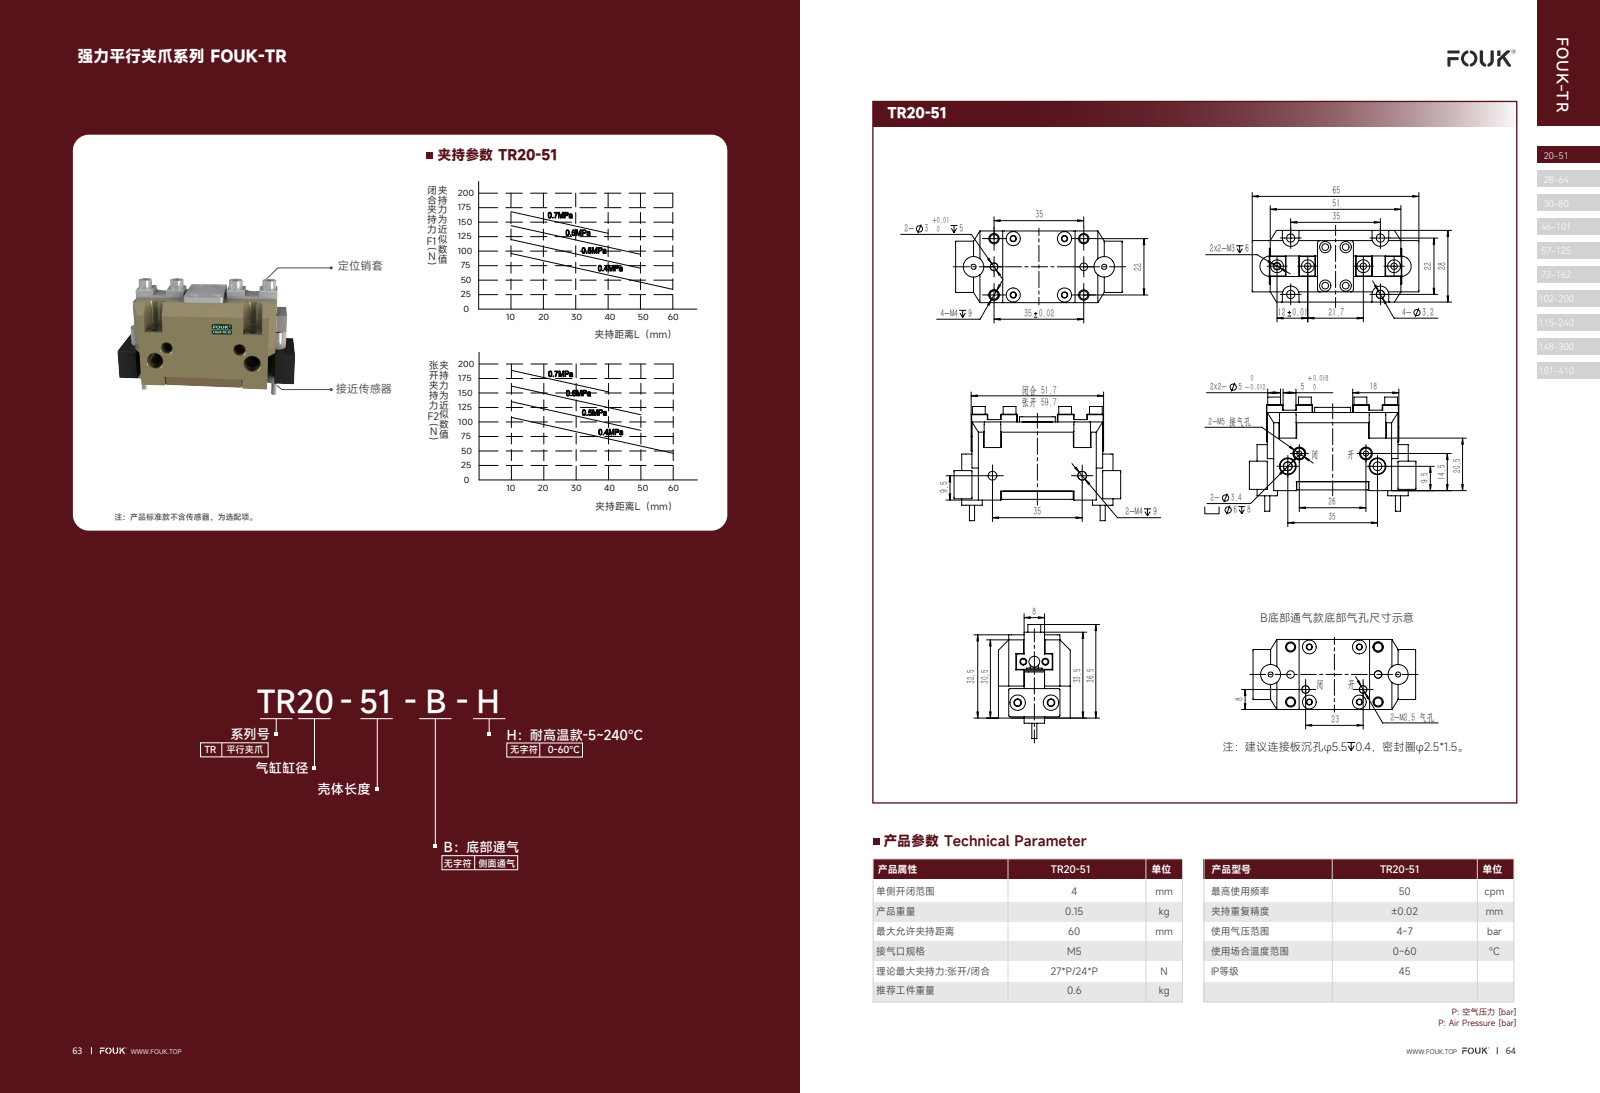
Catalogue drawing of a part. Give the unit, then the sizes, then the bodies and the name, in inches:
Units: inches
Overall size (bounding box): 2.559 × 1.871 × 1.102
Round holes (diameter × count): ⌀0.118 ×7, ⌀0.098 ×6, ⌀0.13 ×6, ⌀0.102 ×5, ⌀0.087 ×4, ⌀0.126 ×4, ⌀0.197 ×4, ⌀0.236 ×4, ⌀0.081 ×3, ⌀0.079 ×2, ⌀0.083 ×2, ⌀0.106 ×2
Round bosses / shafts (diameter × count): ⌀0.079 ×4, ⌀0.15 ×2, ⌀0.063 ×1, ⌀0.028 ×1
Partial cylindrical surfaces — rounded edges, fillets, slot ends (radius × count): R0.005 ×30, R0.079 ×8, R0.039 ×6, R0.012 ×5, R0.02 ×4, R0.128 ×4, R0.006 ×2, R0.02 ×2
Main face-to-face distances: 0.118, 0.276, 0.709, 0.394, 0.433, 0.827, 0.453, 1.102, 0.236, 0.551
Hole centre spacings: 0.903, 0.315, 0.415, 0.433, 0.481, 0.506, 0.535, 0.544
Volume: 2.559 in³ · Surface area: 35.12 in²
Bodies: 20 solids, 1111 faces (593 planar, 257 cylindrical, 261 other)
Part name (STEP PRODUCT): 12x6-R2; TR20-51
STEP written by: SolidWorks 2018 (CONFIG_CONTROL_DESIGN)
